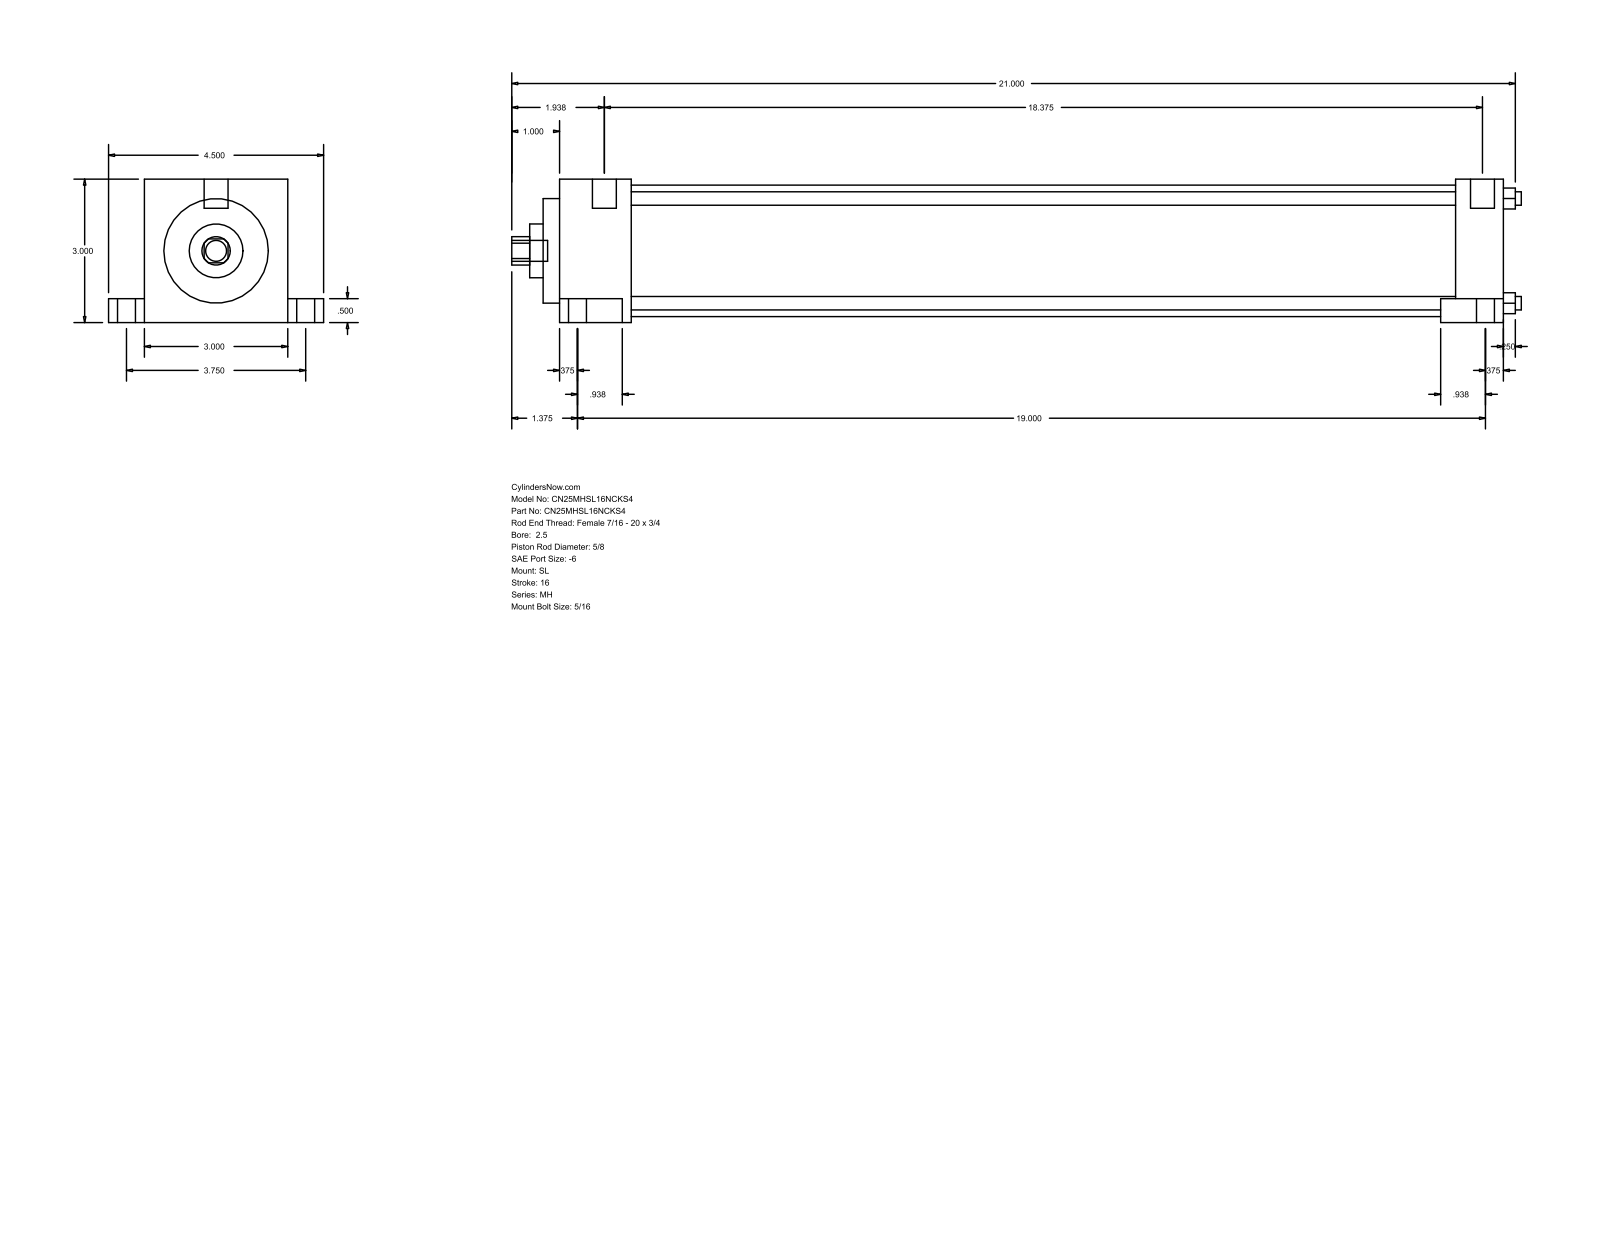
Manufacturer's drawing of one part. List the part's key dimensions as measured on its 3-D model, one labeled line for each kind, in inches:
Part name (STEP PRODUCT): MH_SL__0250_0.625
STEP written by: GSSL Pune (CONFIG_CONTROL_DESIGN)
Units: inches
Bodies: 0 solids, 86 faces (61 planar, 25 cylindrical, 0 other)
Overall size (bounding box): 21.125 × 4.5 × 3
Round holes (diameter × count): ⌀0.281 ×4, ⌀0.625 ×1, ⌀1.125 ×1, ⌀2.187 ×1, ⌀2.75 ×1
Round bosses / shafts (diameter × count): ⌀0.625 ×2, ⌀0.375 ×2, ⌀0.219 ×2, ⌀0.5 ×1, ⌀0.437 ×1
Partial cylindrical surfaces — rounded edges, fillets, slot ends (radius × count): R0.297 ×1
Main face-to-face distances: 3, 1, 19.094, 20.094, 0.5, 2.5, 0.75, 3.75, 1.25, 18.781
Hole centre spacings: 1.548, 2.19, 3.097
